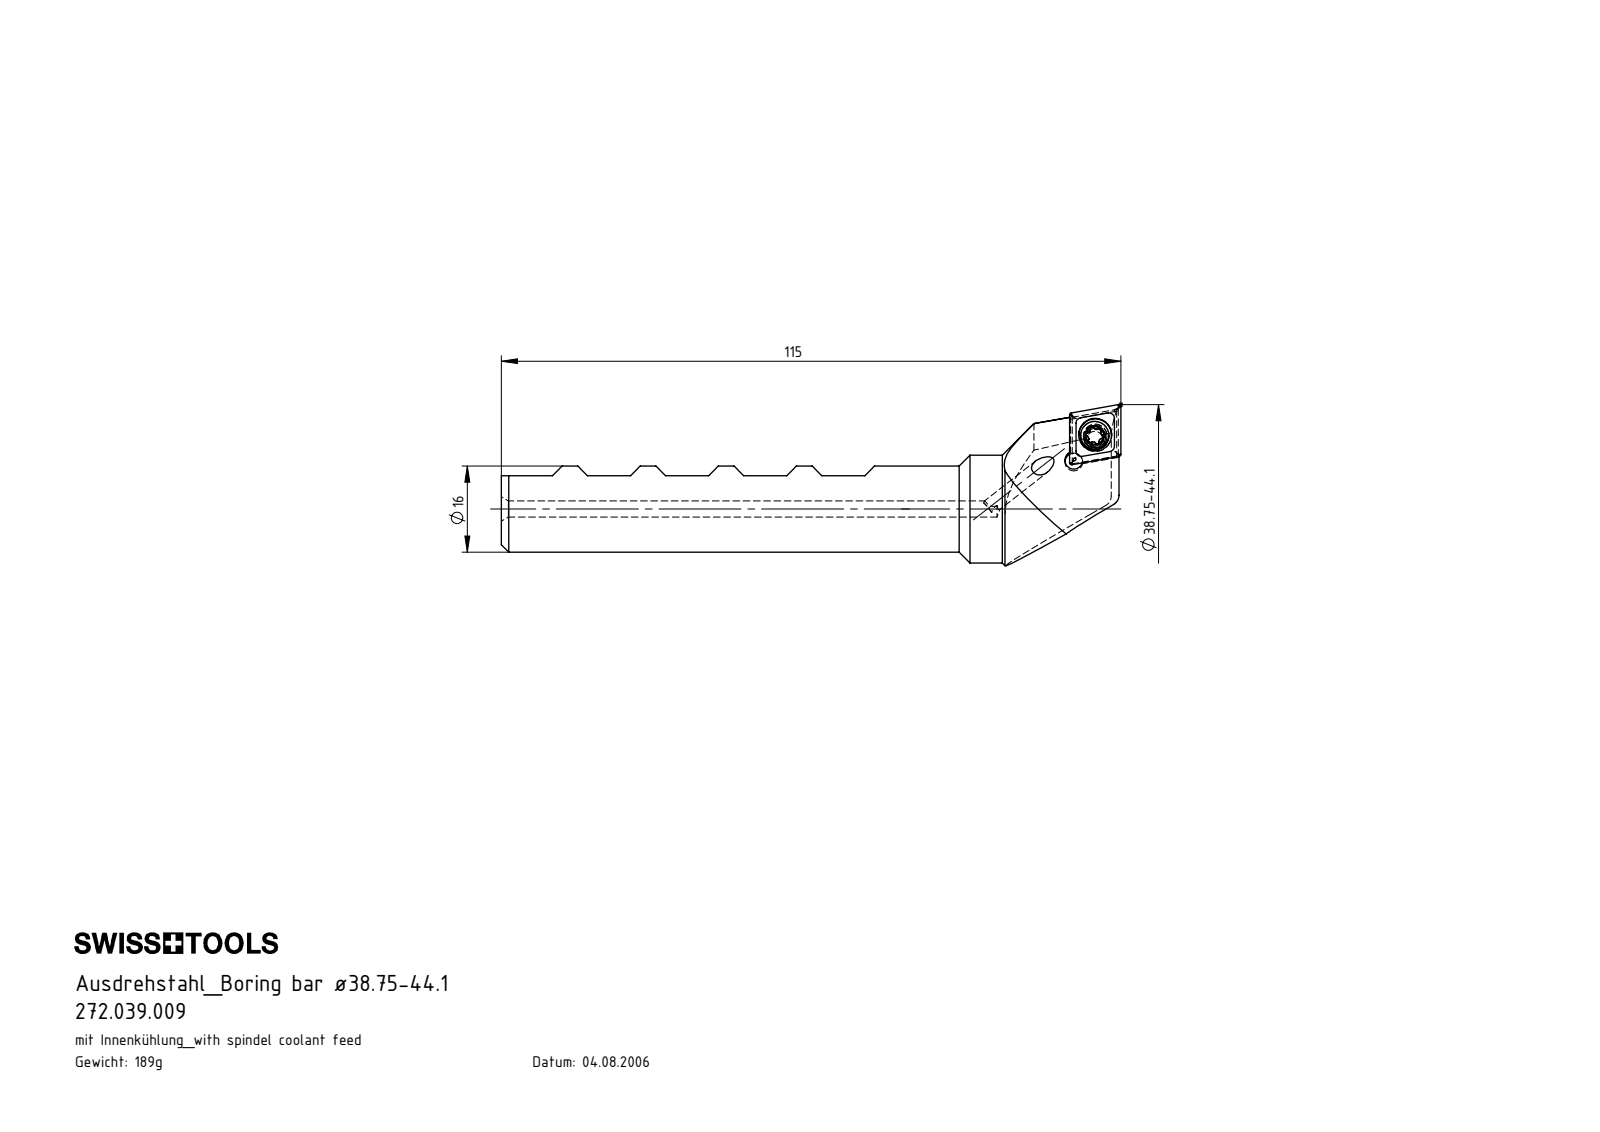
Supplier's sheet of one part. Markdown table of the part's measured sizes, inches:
| quantity | value |
| --- | --- |
| part name | B39-WCB.K11.115; WCB-ER2.001.009_A; CCMT09T304; B39-WCB.K11.115_A |
| STEP written by | SolidWorks 2012 (CONFIG_CONTROL_DESIGN) |
| units | inches |
| bodies | 3 solids, 144 faces (45 planar, 39 cylindrical, 60 other) |
| overall size | 4.528 × 1.176 × 0.877 |
| volume | 1.466 in³ |
| surface area | 12.75 in² |
| round holes (diameter × count) | 0.118 × 2, 0.13 × 2, 0.173 × 1, 0.24 × 1 |
| round bosses / shafts (diameter × count) | 0.787 × 1, 0.63 × 1, 0.207 × 1, 0.157 × 1 |
| partial cylindrical surfaces (radius × count) | 0.013 × 6, 0.023 × 6, 0.079 × 1, 0.413 × 1, 0.472 × 1 |
| main face-to-face distances | 0.324, 0.404, 0.472, 0.148, 0.807, 0.012, 0.807, 1.211, 0.48, 0.156 |
| hole center spacings | 0.239, 0.244 |
